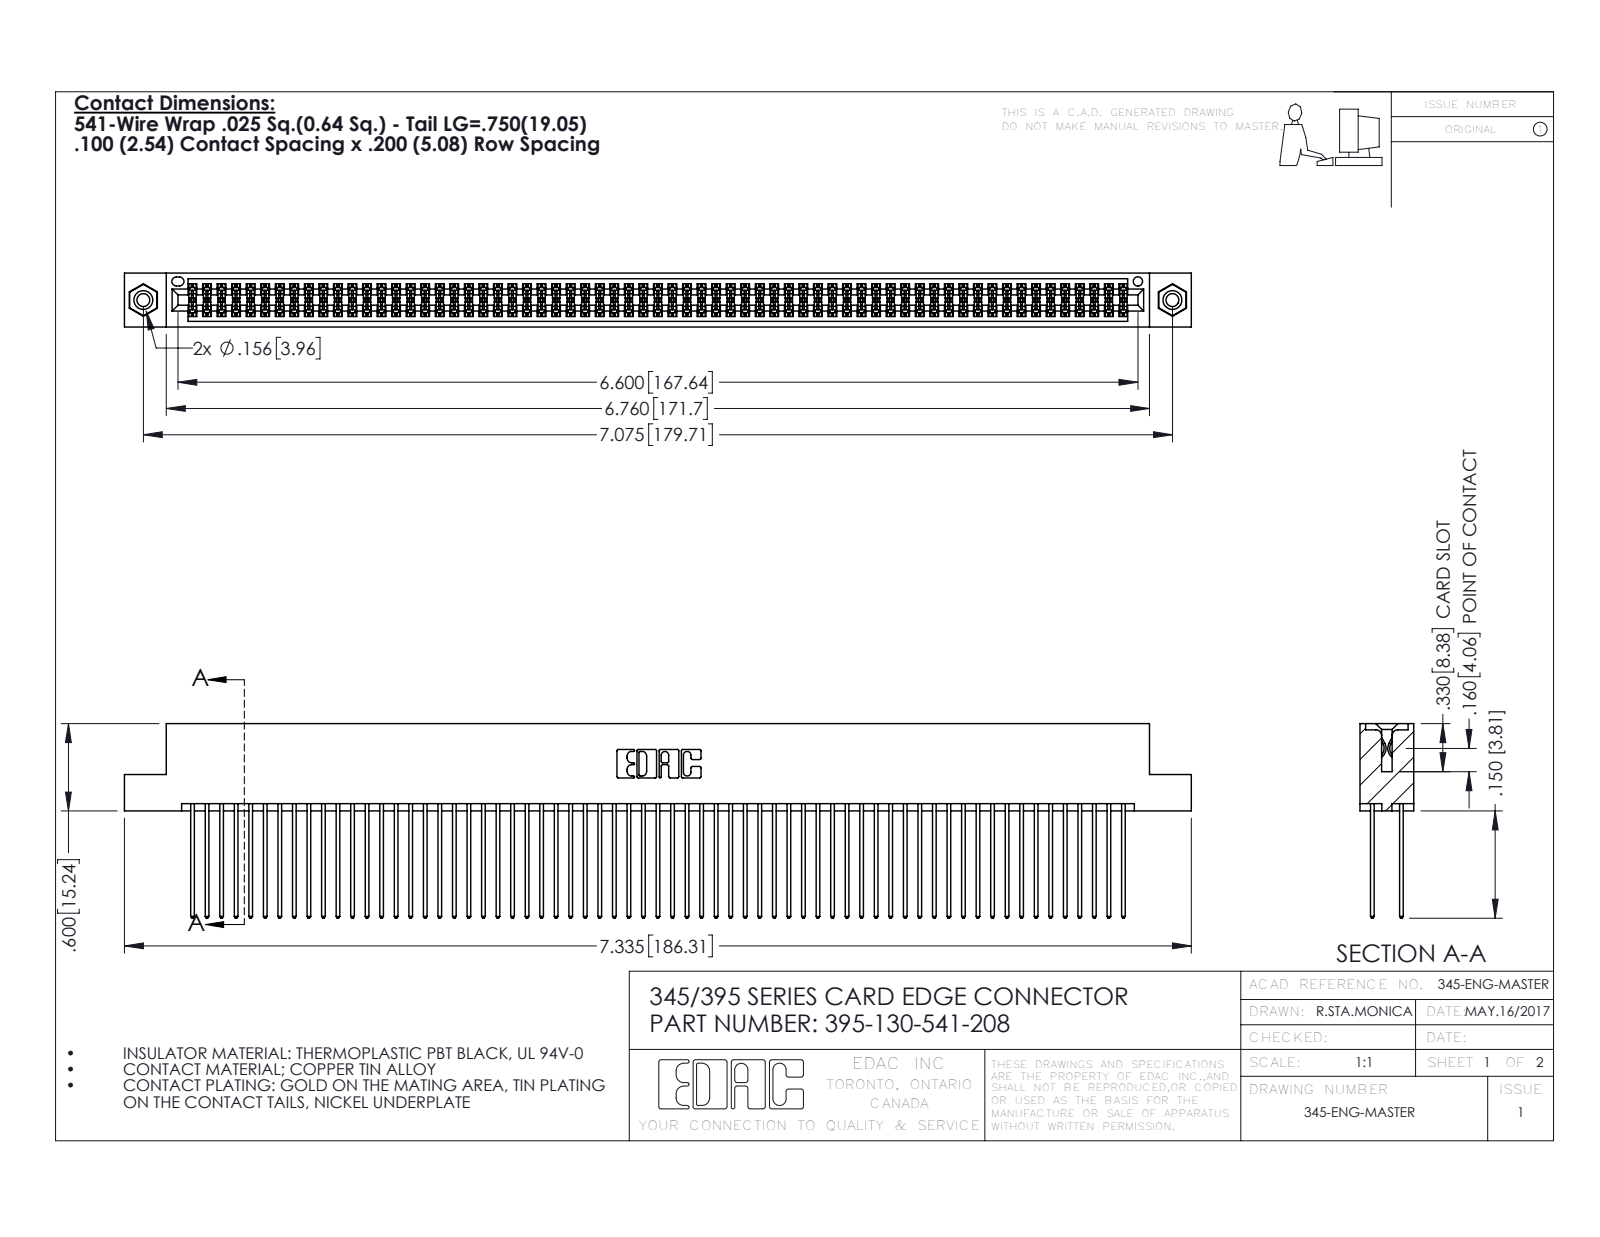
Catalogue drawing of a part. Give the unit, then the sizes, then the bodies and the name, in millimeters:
Units: millimetres
Overall size (bounding box): 186.3 × 34 × 9.4
Round holes (diameter × count): ⌀2.3 ×2, ⌀3.2 ×2, ⌀4 ×2, ⌀1.6 ×1
Round bosses / shafts (diameter × count): ⌀3.9 ×2
Partial cylindrical surfaces — rounded edges, fillets, slot ends (radius × count): R0.2 ×195, R0.3 ×130, R0.3 ×22, R0.2 ×6, R0.8 ×6, R0.7 ×3, R0.4 ×2, R0.5 ×2
Main face-to-face distances: 1.8, 7.6, 5.1, 2.5, 6.9, 0.6, 5.7, 9.4, 4.4, 3.8
Hole centre spacings: 6.9, 173.7, 179.7
Volume: 19 060 mm³ · Surface area: 32 120 mm²
Bodies: 133 solids, 6686 faces (4402 planar, 2268 cylindrical, 16 other)
Part name (STEP PRODUCT): 345 Part_Flush Mounting Lugs - 0.156 Dia-TI; 345-292-001_345-293-141; 345-250-001_345-250-003-102; 395-130-541-208
STEP written by: SolidWorks 2016 (CONFIG_CONTROL_DESIGN)
